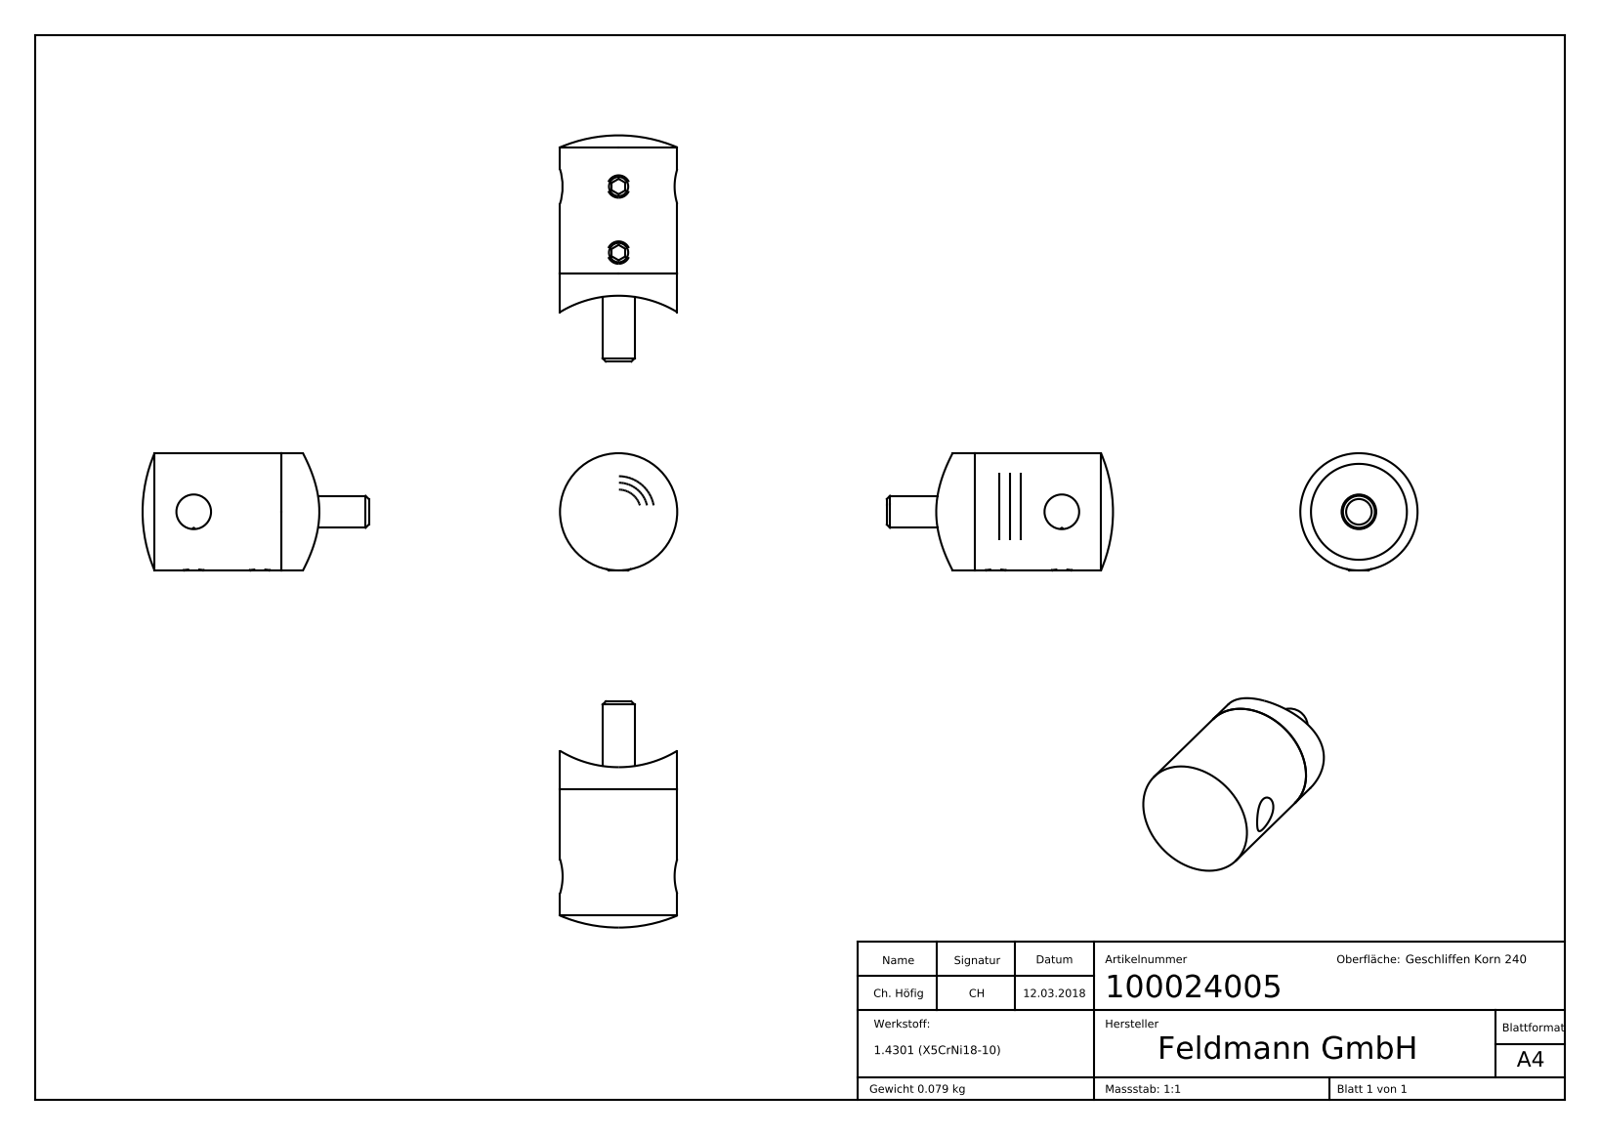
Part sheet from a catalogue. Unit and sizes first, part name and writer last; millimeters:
Units: millimetres
Overall size (bounding box): 42.45 × 24 × 22
Round holes (diameter × count): ⌀4.2 ×2, ⌀6.5 ×2, ⌀12.1 ×1, ⌀18 ×1
Round bosses / shafts (diameter × count): ⌀5 ×2, ⌀22 ×1, ⌀12 ×1, ⌀6 ×1
Partial cylindrical surfaces — rounded edges, fillets, slot ends (radius × count): R21.2 ×1
Main face-to-face distances: 2, 10.55, 8.55, 4, 14.45, 16.45, 25, 2.5, 10.73, 23.95
Hole centre spacings: 12.4
Volume: 9 920 mm³ · Surface area: 5 914 mm²
Bodies: 5 solids, 281 faces (145 planar, 15 cylindrical, 121 other)
Part name (STEP PRODUCT): 100024005; DIN7991 M6x25_DIN7991 M6x25; 10002X00X Teil1_10002X005 Teil1; DIN7991 M6x25 (+6 more)
STEP written by: SolidWorks 2018 (CONFIG_CONTROL_DESIGN)
